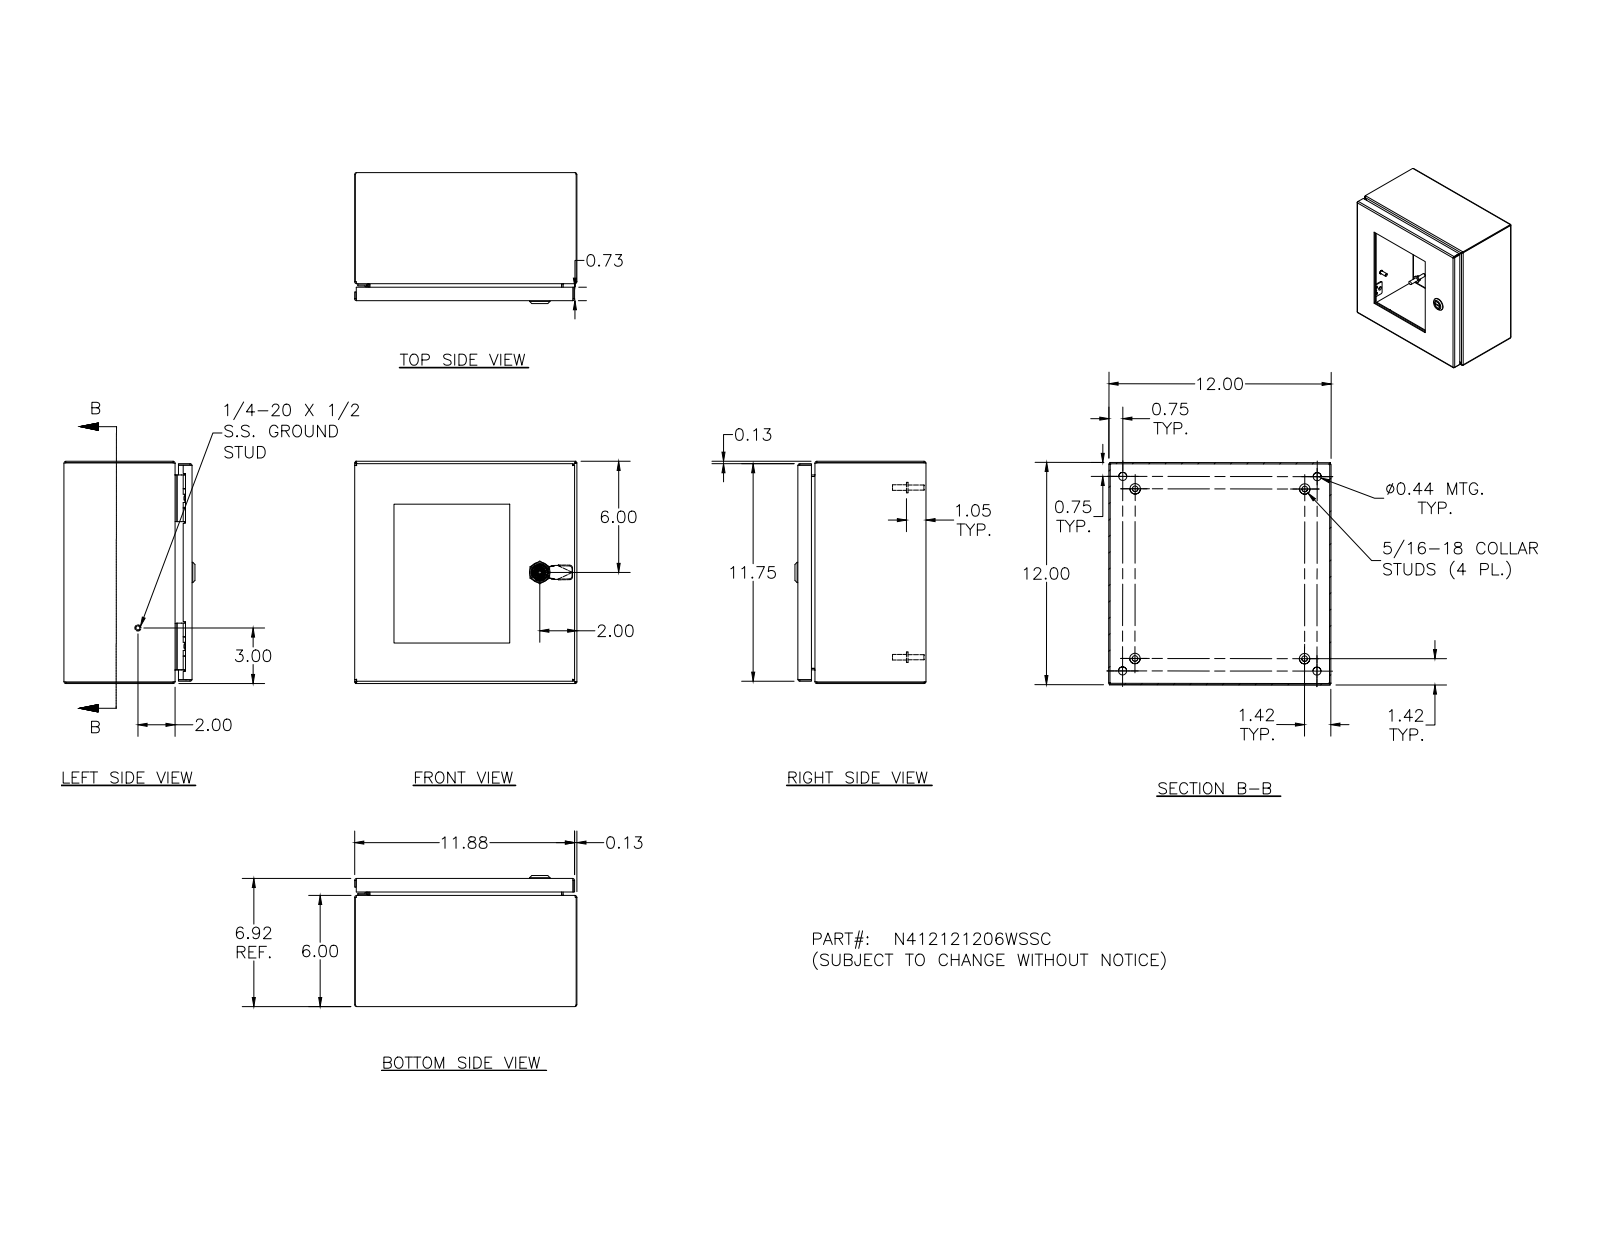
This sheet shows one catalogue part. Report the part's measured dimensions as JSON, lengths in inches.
{"part_name": "N412121206WSSC; N412121206WSSCBKP; N4121212WSSCLID; HFW328176 (+8 more)", "step_written_by": "Autodesk Inventor 2011 (AUTOMOTIVE_DESIGN)", "units": "inches", "bodies": {"solids": 54, "faces": 1684, "planar": 666, "cylindrical": 533, "other": 485}, "overall_size": [12, 12, 7.075], "volume_in3": 65.2, "surface_area_in2": 1499, "round_holes": [[0.156, 10], [0.281, 8], [0.093, 4], [0.152, 4], [0.167, 4], [0.172, 4], [0.188, 4], [0.437, 4], [0.187, 1], [0.197, 1], [0.315, 1], [0.394, 1]], "round_bosses_or_shafts": [[0.25, 10], [0.19, 8], [0.253, 7], [0.563, 4], [0.36, 4], [0.32, 4], [0.3, 4], [0.275, 4]], "partial_cylinders_radius": [[0.031, 34], [0.05, 26], [0.105, 24], [0.016, 18], [0.125, 16], [0.02, 9], [0.032, 8], [0.157, 4]], "face_to_face_distances": [0.074, 11.926, 6.843, 6.769, 11.852, 12, 6.917, 0.25, 6.593, 6.519], "hole_center_spacings": [8, 4, 6.221, 8.585, 10.5, 8.927, 0.5, 0.656]}
